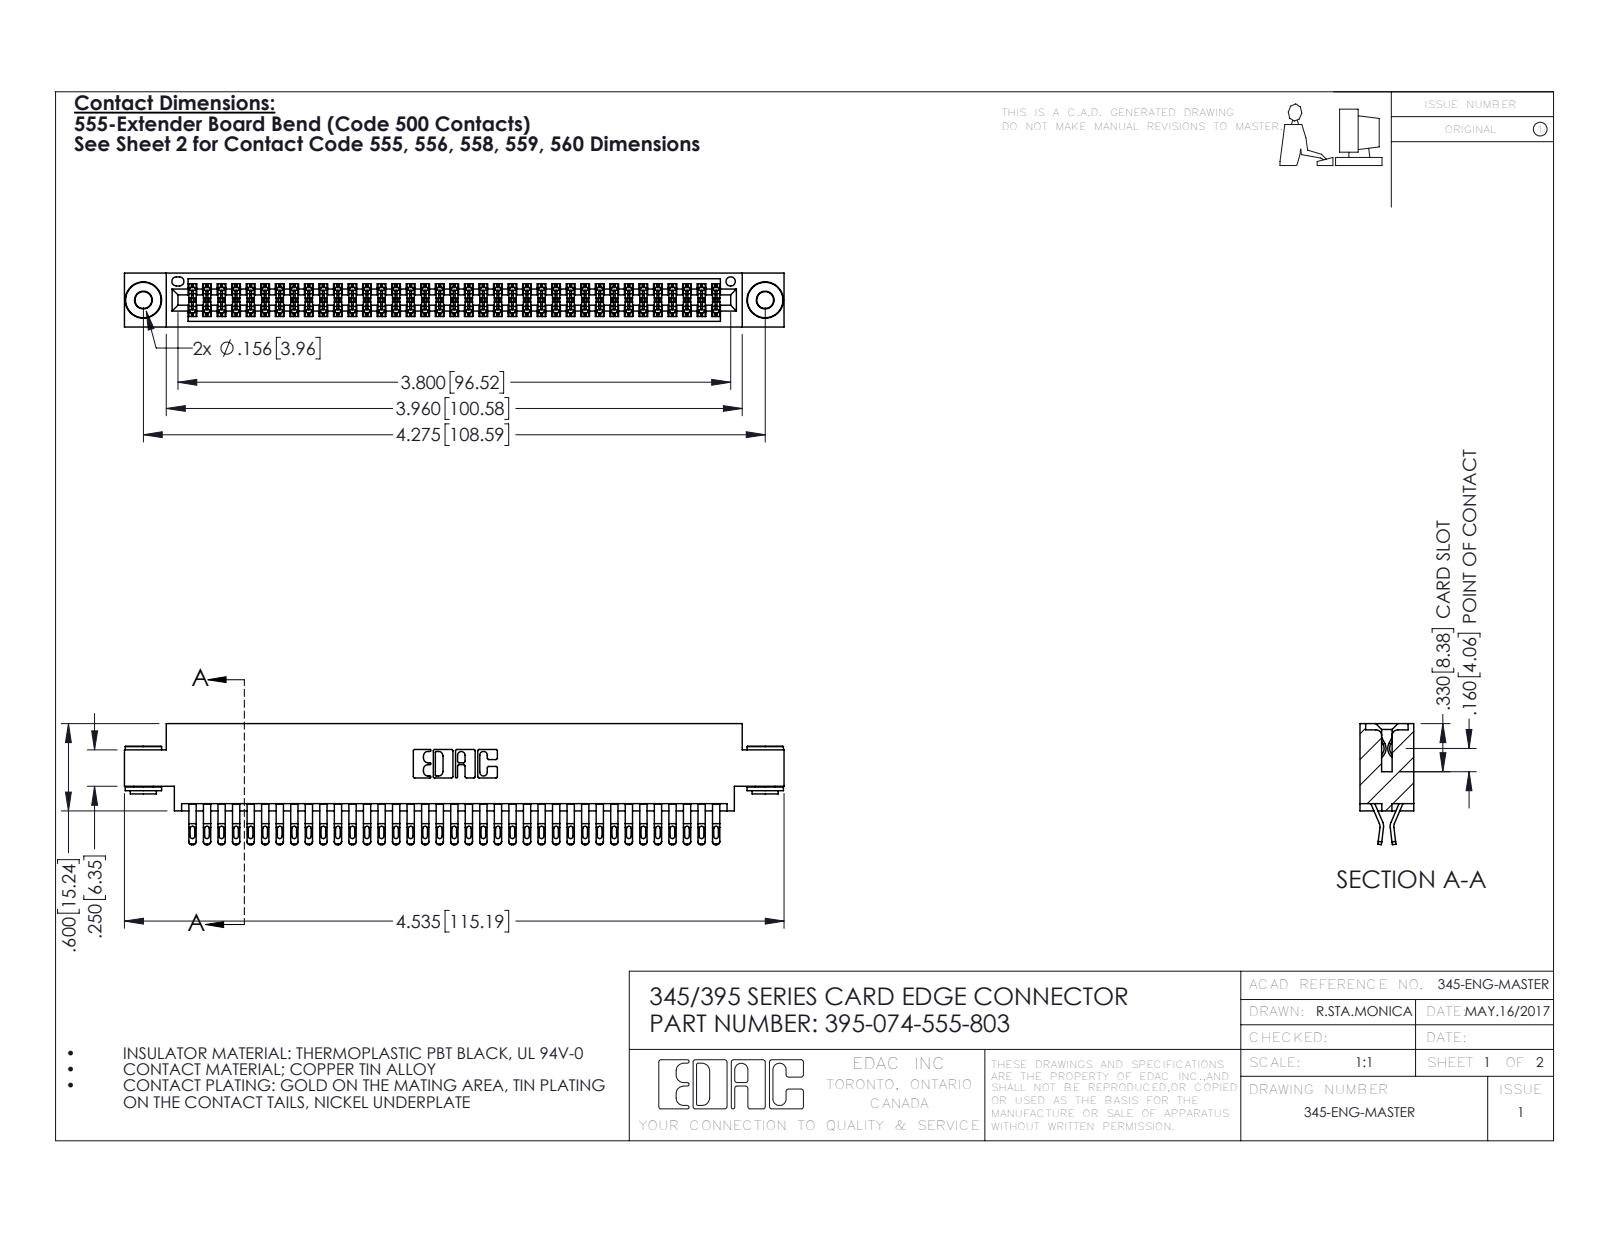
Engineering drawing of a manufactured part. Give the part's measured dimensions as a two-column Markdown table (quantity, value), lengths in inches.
| quantity | value |
| --- | --- |
| part name | 345 Part_0.170 Offset - 0.156 Dia-TH; 395-074-555-803; 345-292-001_555 Tail; 345-250-002_345-250-002-102 |
| STEP written by | SolidWorks 2016 (CONFIG_CONTROL_DESIGN) |
| units | inches |
| bodies | 77 solids, 4312 faces (2388 planar, 1916 cylindrical, 8 other) |
| overall size | 4.535 × 0.832 × 0.37 |
| volume | 0.687 in³ |
| surface area | 27.35 in² |
| round holes (diameter × count) | 0.116 × 2, 0.156 × 2, 0.064 × 1 |
| round bosses / shafts (diameter × count) | 0.25 × 2, 0.18 × 2, 0.136 × 2 |
| partial cylindrical surfaces (radius × count) | 0.016 × 185, 0.02 × 148, 0.006 × 111, 0.01 × 22, 0.007 × 6, 0.031 × 6, 0.026 × 3, 0.01 × 2 |
| main face-to-face distances | 0.072, 0.298, 0.37, 0.025, 0.2, 0.098, 0.272, 0.225, 0.175, 0.149 |
| hole center spacings | 0.27, 4.039, 4.275 |
